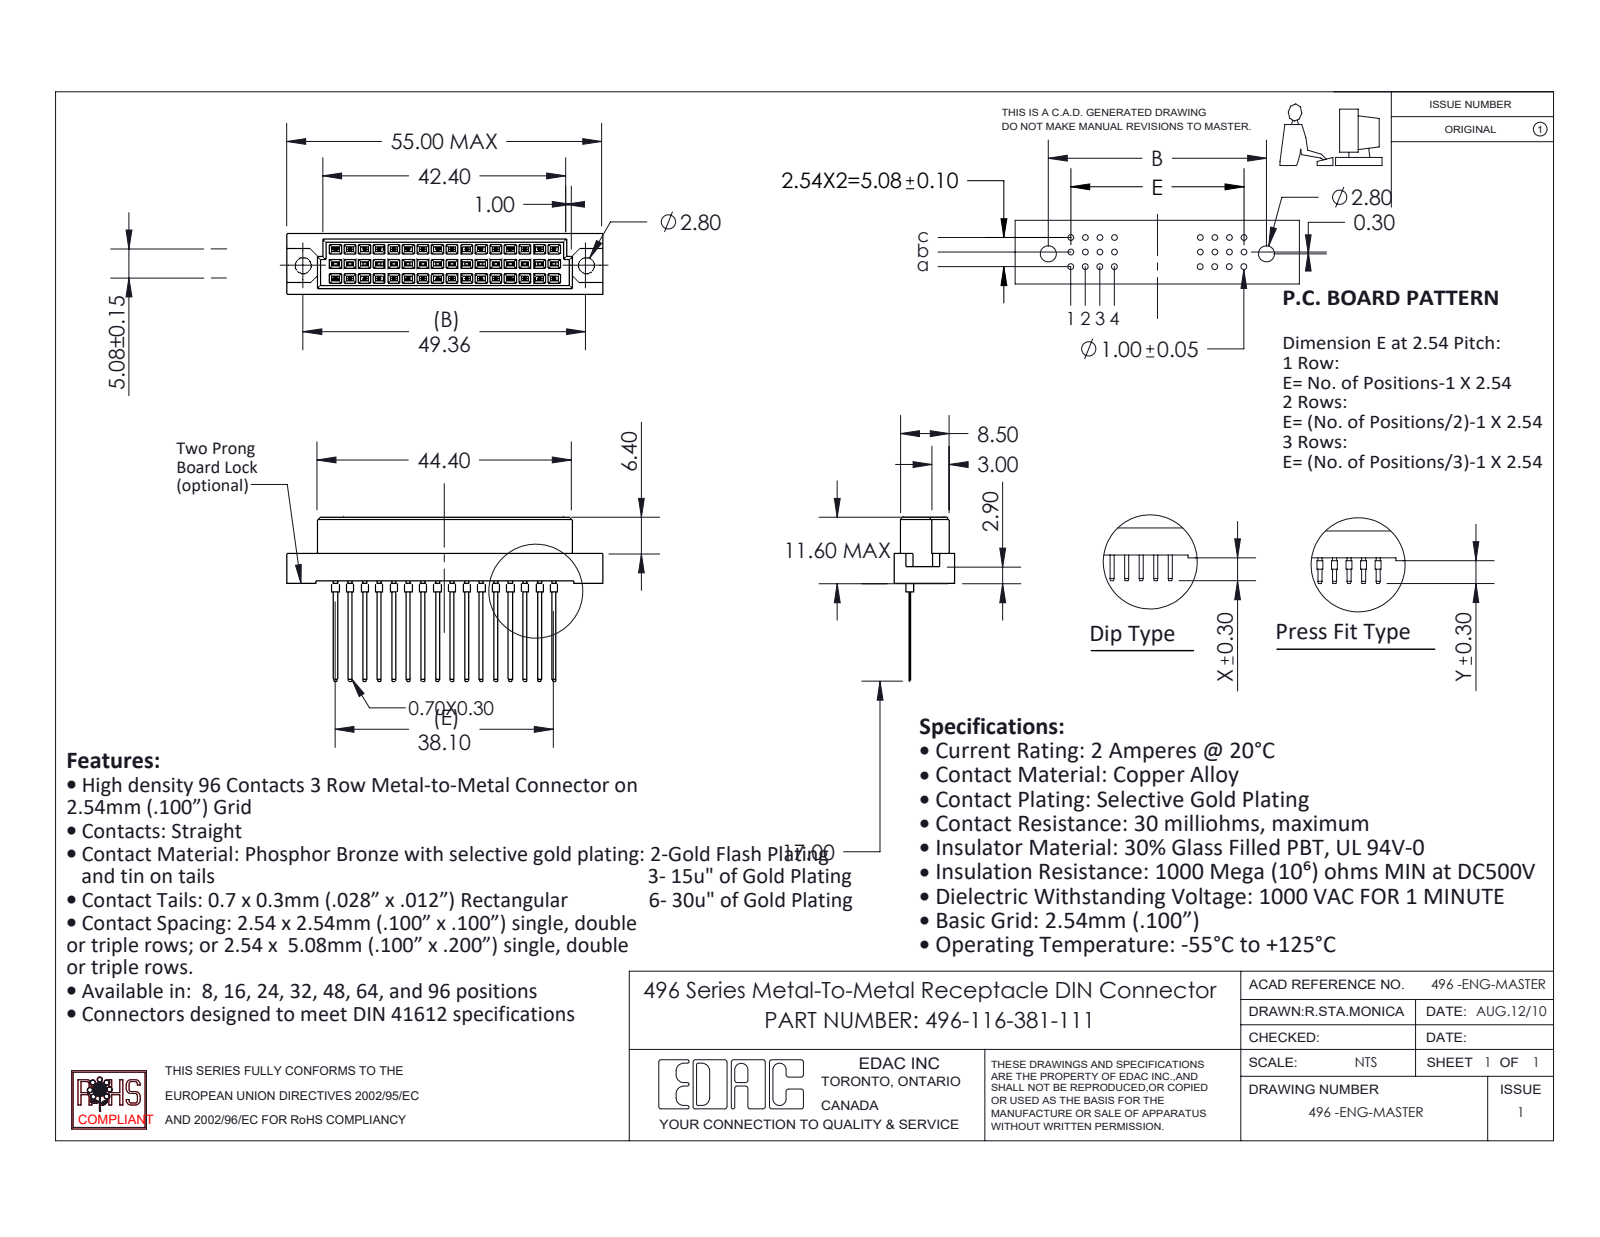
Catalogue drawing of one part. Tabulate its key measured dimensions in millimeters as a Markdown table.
| quantity | value |
| --- | --- |
| part name | 496-290_81; 496-116-381-111; 496 Part_48 |
| STEP written by | SolidWorks 2020 (CONFIG_CONTROL_DESIGN) |
| units | millimeters |
| bodies | 17 solids, 954 faces (918 planar, 36 cylindrical, 0 other) |
| overall size | 55 × 28.6 × 10.6 |
| volume | 4 675 mm³ |
| surface area | 4 949 mm² |
| round holes (diameter × count) | 2.8 × 2 |
| round bosses / shafts (diameter × count) | 1 × 16 |
| main face-to-face distances | 2.54, 5.08, 1.05, 9.55, 0.81, 2.91, 7.69, 2.61, 7.99, 1.86 |
| hole center spacings | 49.36 |
